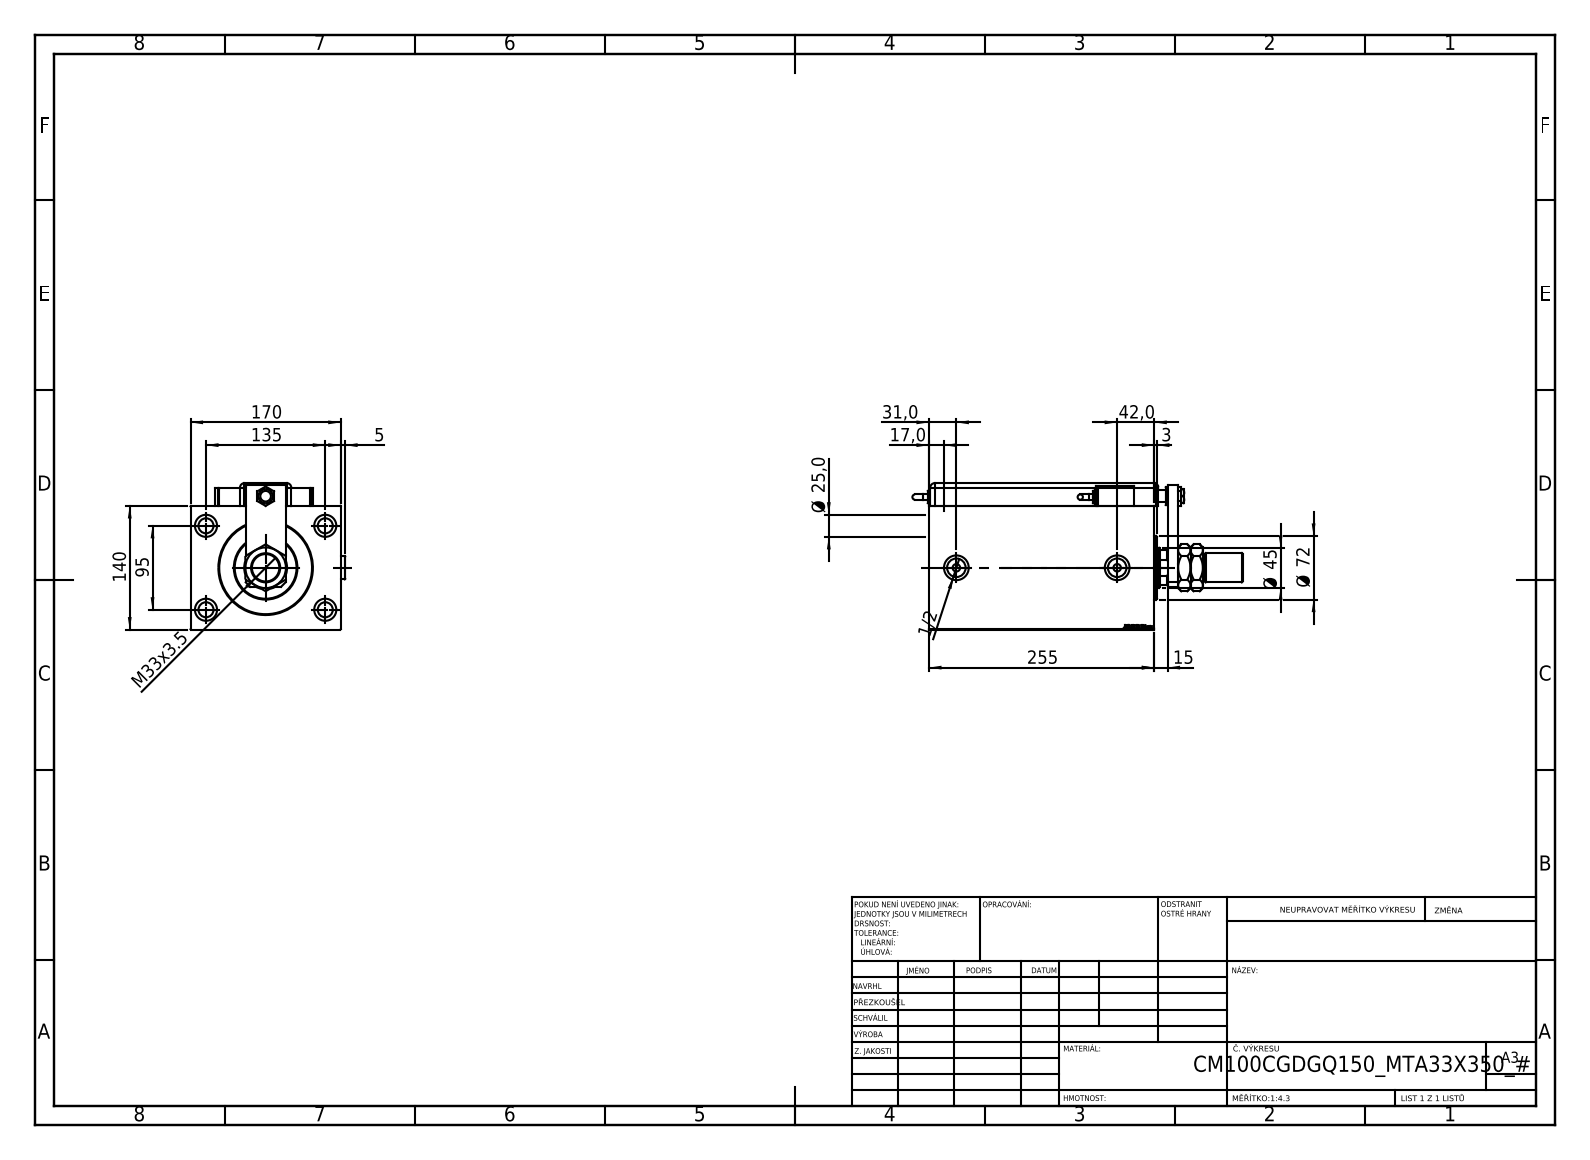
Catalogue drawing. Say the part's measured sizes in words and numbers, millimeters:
The part is named "Q_T_W_MTA; ZARAZKA_Q; Zatka_OIL_PORT; SWITCH Q (+8 more)". Its 3-D file was written by "SolidWorks 2019 (CONFIG_CONTROL_DESIGN)". It is 16 solids with 1352 faces: 664 planar, 137 cylindrical and 551 other. Overall it measures 373.76 by 174.9 by 165.8 millimeters. Its volume is 5 179 000 cubic millimeters and its surface area 542 459 square millimeters. Round holes: 4 of diameter 17, 4 of diameter 25, 2 of diameter 4, 2 of diameter 8, 2 of diameter 8.5, 2 of diameter 20.96, 2 of diameter 28, 1 of diameter 12, 1 of diameter 13, 1 of diameter 14, 1 of diameter 31.5, 1 of diameter 33. Round bosses or shafts: 3 of diameter 20, 2 of diameter 26, 2 of diameter 16, 2 of diameter 14, 2 of diameter 6, 1 of diameter 72, 1 of diameter 31. Partial cylindrical surfaces (rounded edges, fillets, slot ends): 9 of radius 5, 1 of radius 10, 1 of radius 22. The main face-to-face distances are 140, 170, 3, 255, 26, 229, 15, 25.8, 165.8, 162.8. The hole center spacings are 82.54, 75.36, 95, 135, 145.15, 165.08, 20, 81.
